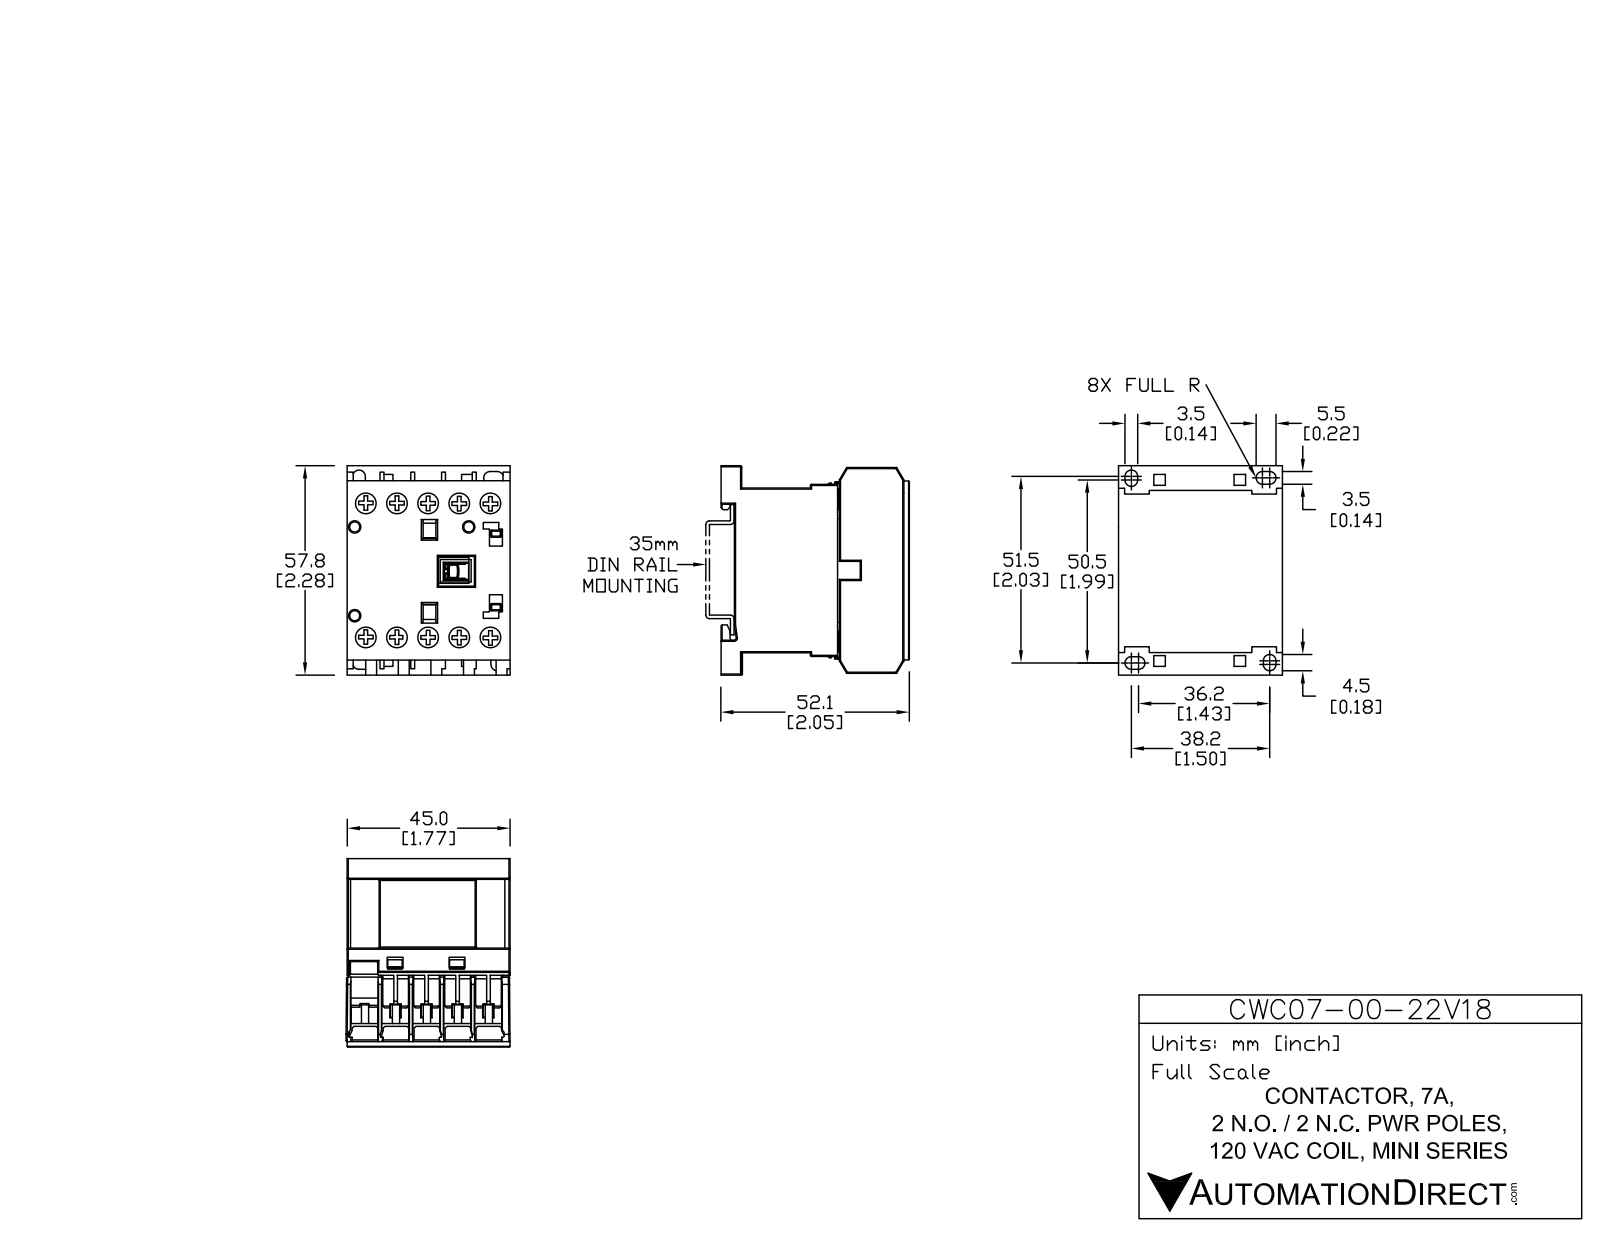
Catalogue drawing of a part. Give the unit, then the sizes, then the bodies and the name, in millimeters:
Units: millimetres
Overall size (bounding box): 58.04 × 52.12 × 45.75
Round holes (diameter × count): ⌀6.2 ×10, ⌀2.8 ×3
Round bosses / shafts (diameter × count): ⌀5.9 ×10
Partial cylindrical surfaces — rounded edges, fillets, slot ends (radius × count): R0.3 ×20, R1.72 ×6, R1.73 ×2, R0.32 ×1, R0.42 ×1, R0.55 ×1
Main face-to-face distances: 8.25, 45.5, 1.25, 16.5, 9.5, 5.5, 17.75, 5.13, 10.63, 7
Hole centre spacings: 8.55, 37.94, 17.1, 40.72, 36.96, 25.65, 44.99, 6.91
Volume: 97 133 mm³ · Surface area: 30 437 mm²
Bodies: 15 solids, 535 faces (445 planar, 90 cylindrical, 0 other)
Part name (STEP PRODUCT): CWC07-00-22V18
STEP written by: SolidWorks 2013 (AUTOMOTIVE_DESIGN)
